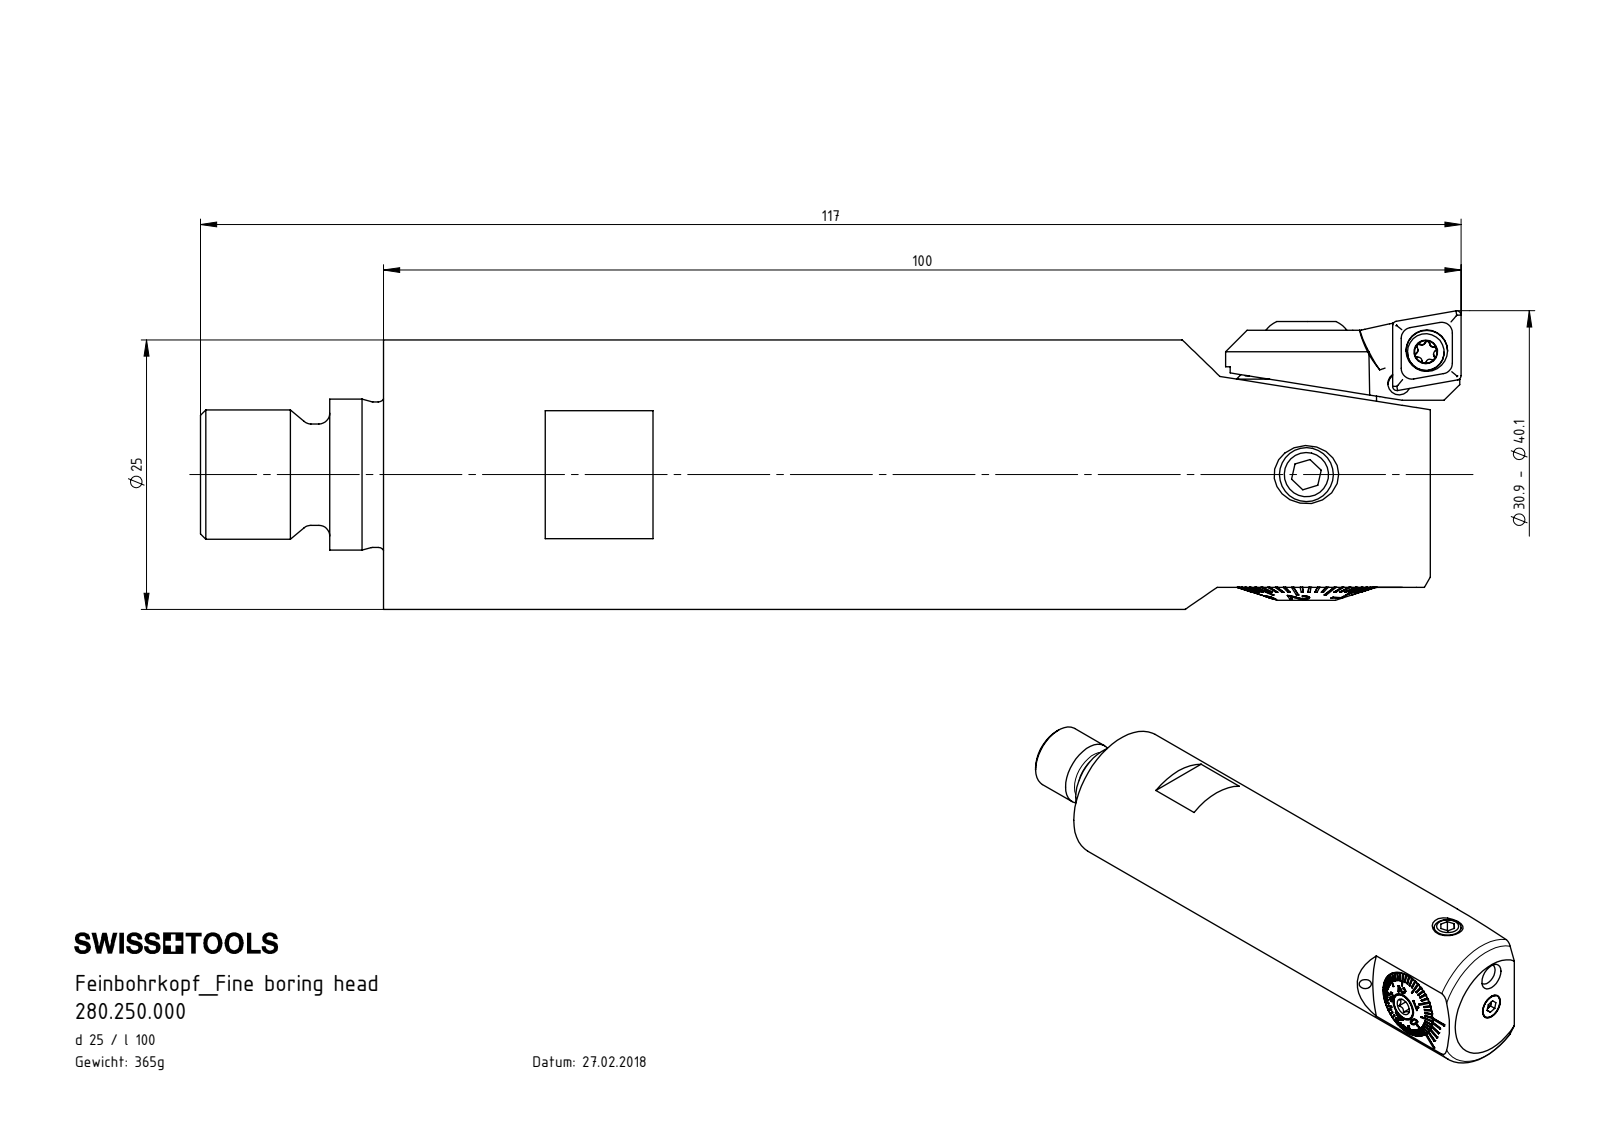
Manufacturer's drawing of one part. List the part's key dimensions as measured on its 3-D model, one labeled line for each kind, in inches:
Part name (STEP PRODUCT): WCA-ER2.001.006_A; CCMT060204; F25-WCA.001.006_C_fertigbearbeitet; T7 M2.5 x 6 (+8 more)
STEP written by: SolidWorks 2017 (CONFIG_CONTROL_DESIGN)
Units: inches
Bodies: 16 solids, 790 faces (347 planar, 146 cylindrical, 297 other)
Overall size (bounding box): 4.606 × 1.091 × 0.984
Volume: 2.837 in³ · Surface area: 26.06 in²
Round holes (diameter × count): ⌀0.079 ×4, ⌀0.081 ×2, ⌀0.165 ×2, ⌀0.197 ×2, ⌀0.083 ×1, ⌀0.094 ×1, ⌀0.106 ×1, ⌀0.11 ×1, ⌀0.118 ×1, ⌀0.152 ×1, ⌀0.217 ×1, ⌀0.252 ×1
Round bosses / shafts (diameter × count): ⌀0.197 ×2, ⌀0.195 ×2, ⌀0.098 ×2, ⌀0.984 ×1, ⌀0.551 ×1, ⌀0.531 ×1, ⌀0.511 ×1, ⌀0.506 ×1
Partial cylindrical surfaces — rounded edges, fillets, slot ends (radius × count): R0.008 ×6, R0.014 ×5, R0.02 ×4, R0.052 ×2, R0.008 ×1, R0.014 ×1, R0.041 ×1, R0.049 ×1
Main face-to-face distances: 3.825, 0.059, 0.785, 0.122, 0.618, 0.031, 0.772, 0.154, 0.866, 0.74
Hole centre spacings: 0.151, 0.157, 0.161, 0.268, 0.35
